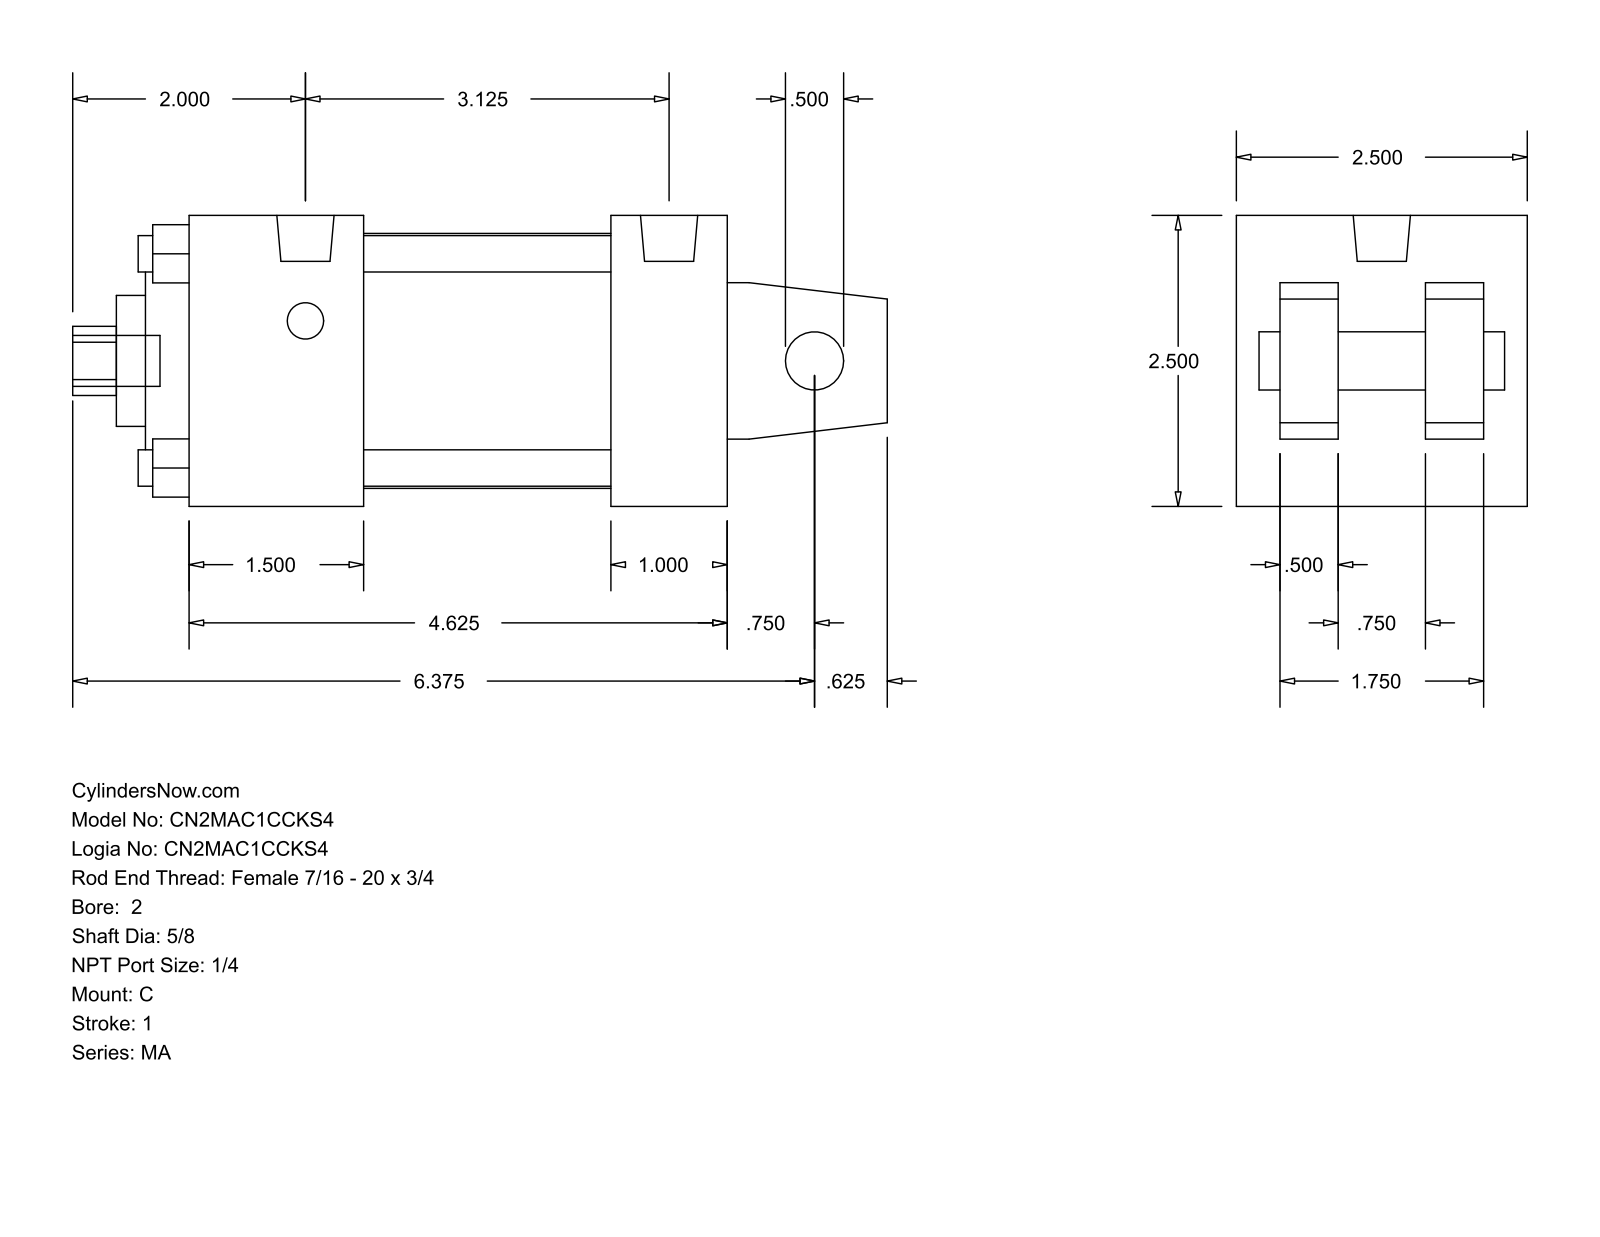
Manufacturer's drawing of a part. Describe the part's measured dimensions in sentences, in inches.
The part is named "MA_C__0200_0.625". Its 3-D file was written by "GSSL Pune (CONFIG_CONTROL_DESIGN)". It is 0 solids with 105 faces: 77 planar, 28 cylindrical and 0 other. Overall it measures 7 by 2.5 by 2.5 inches. Round holes: 4 of diameter 0.313, 1 of diameter 0.5, 1 of diameter 0.625, 1 of diameter 1.125, 1 of diameter 2, 1 of diameter 2.19. Round bosses or shafts: 4 of diameter 0.313, 2 of diameter 0.492, 1 of diameter 0.437. Partial cylindrical surfaces (rounded edges, fillets, slot ends): 1 of radius 0.297. The main face-to-face distances are 2.5, 0.375, 0.5, 0.875, 1.625, 2.125, 1.25, 2.125, 1.5, 4.625. The hole center spacings are 1.301, 1.84, 2.602.
